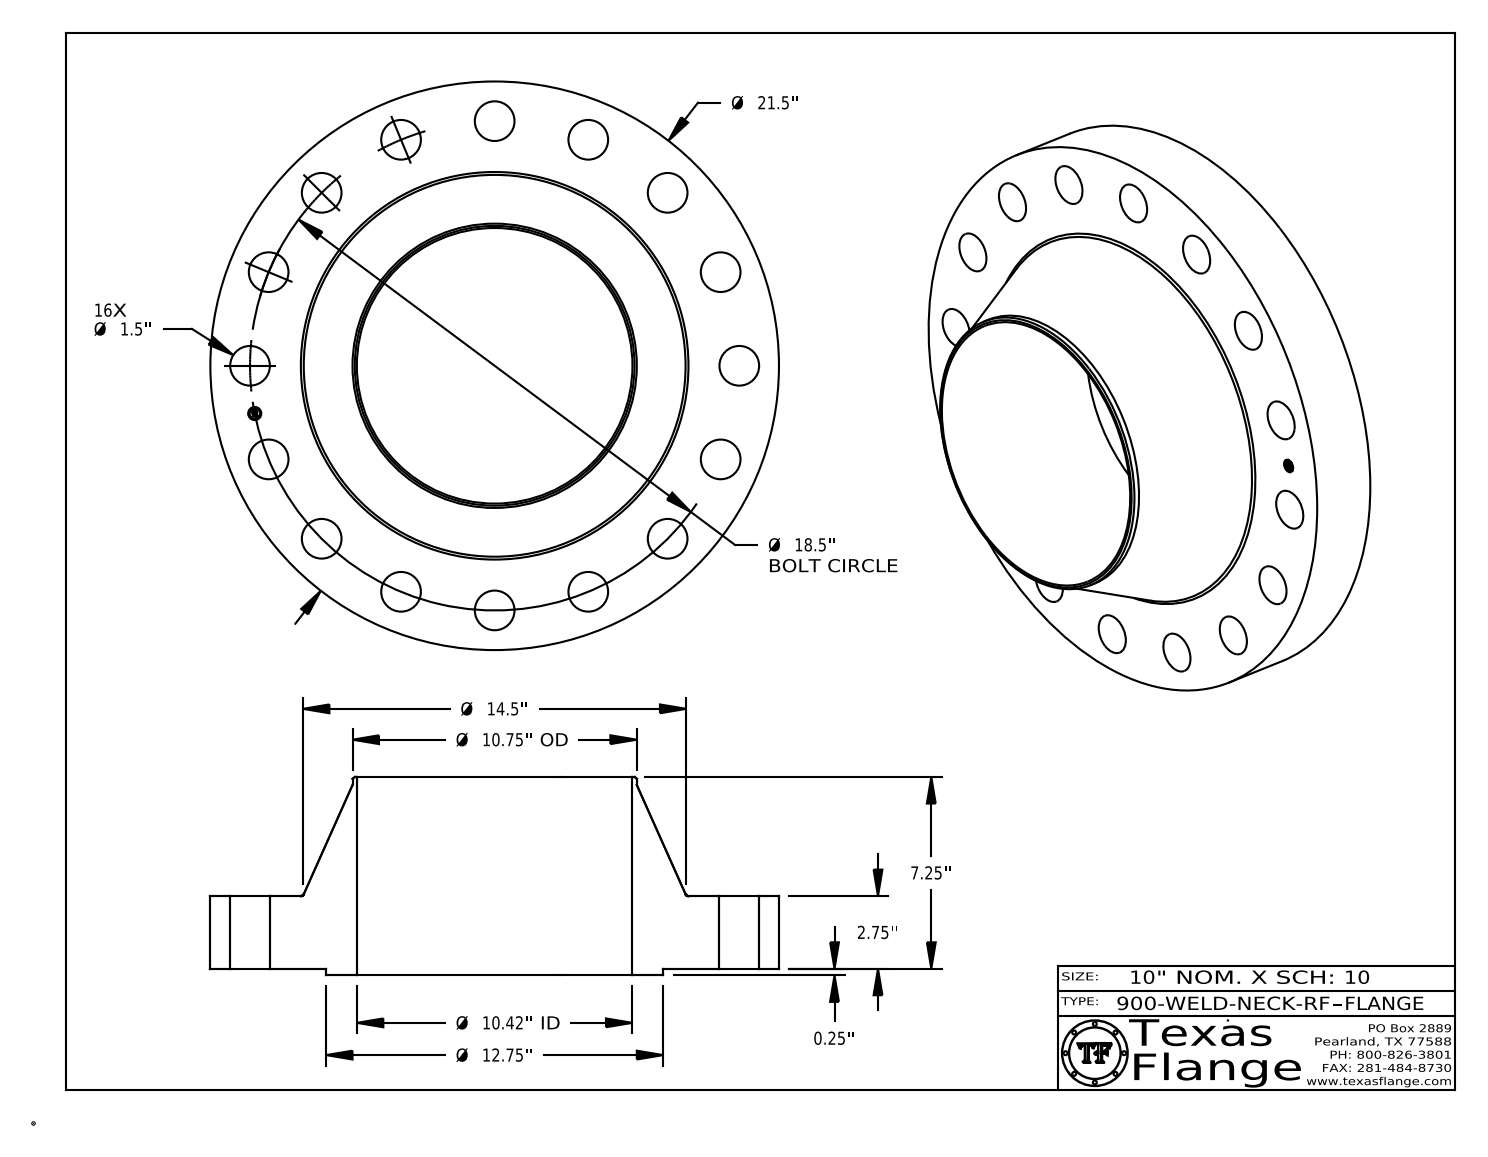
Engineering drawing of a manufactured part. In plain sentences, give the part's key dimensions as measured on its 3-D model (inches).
The part is named "900-WELD-NECK-RF". Its 3-D file was written by "CATIA V5 STEP AP214 (AUTOMOTIVE_DESIGN)". It is 1 solid with 435 faces: 369 planar, 60 cylindrical and 6 other. Overall it measures 21.5 by 21.5 by 7.5 inches. Its volume is 869.7 cubic inches and its surface area 1 264 square inches. Round holes: 16 of diameter 1.5, 1 of diameter 0.495, 1 of diameter 10.42. Round bosses or shafts: 8 of diameter 0.03, 1 of diameter 21.5, 1 of diameter 12.75, 1 of diameter 10.75, 1 of diameter 0.39. The main face-to-face distances are 2.75, 0.25, 3, 7.5, 7.25, 4.5, 2.985, 2.735, 0.015, 4.515. The hole center spacings are 15.382, 7.08, 9.25, 13.081, 3.609, 3.609, 10.278, 10.278.
